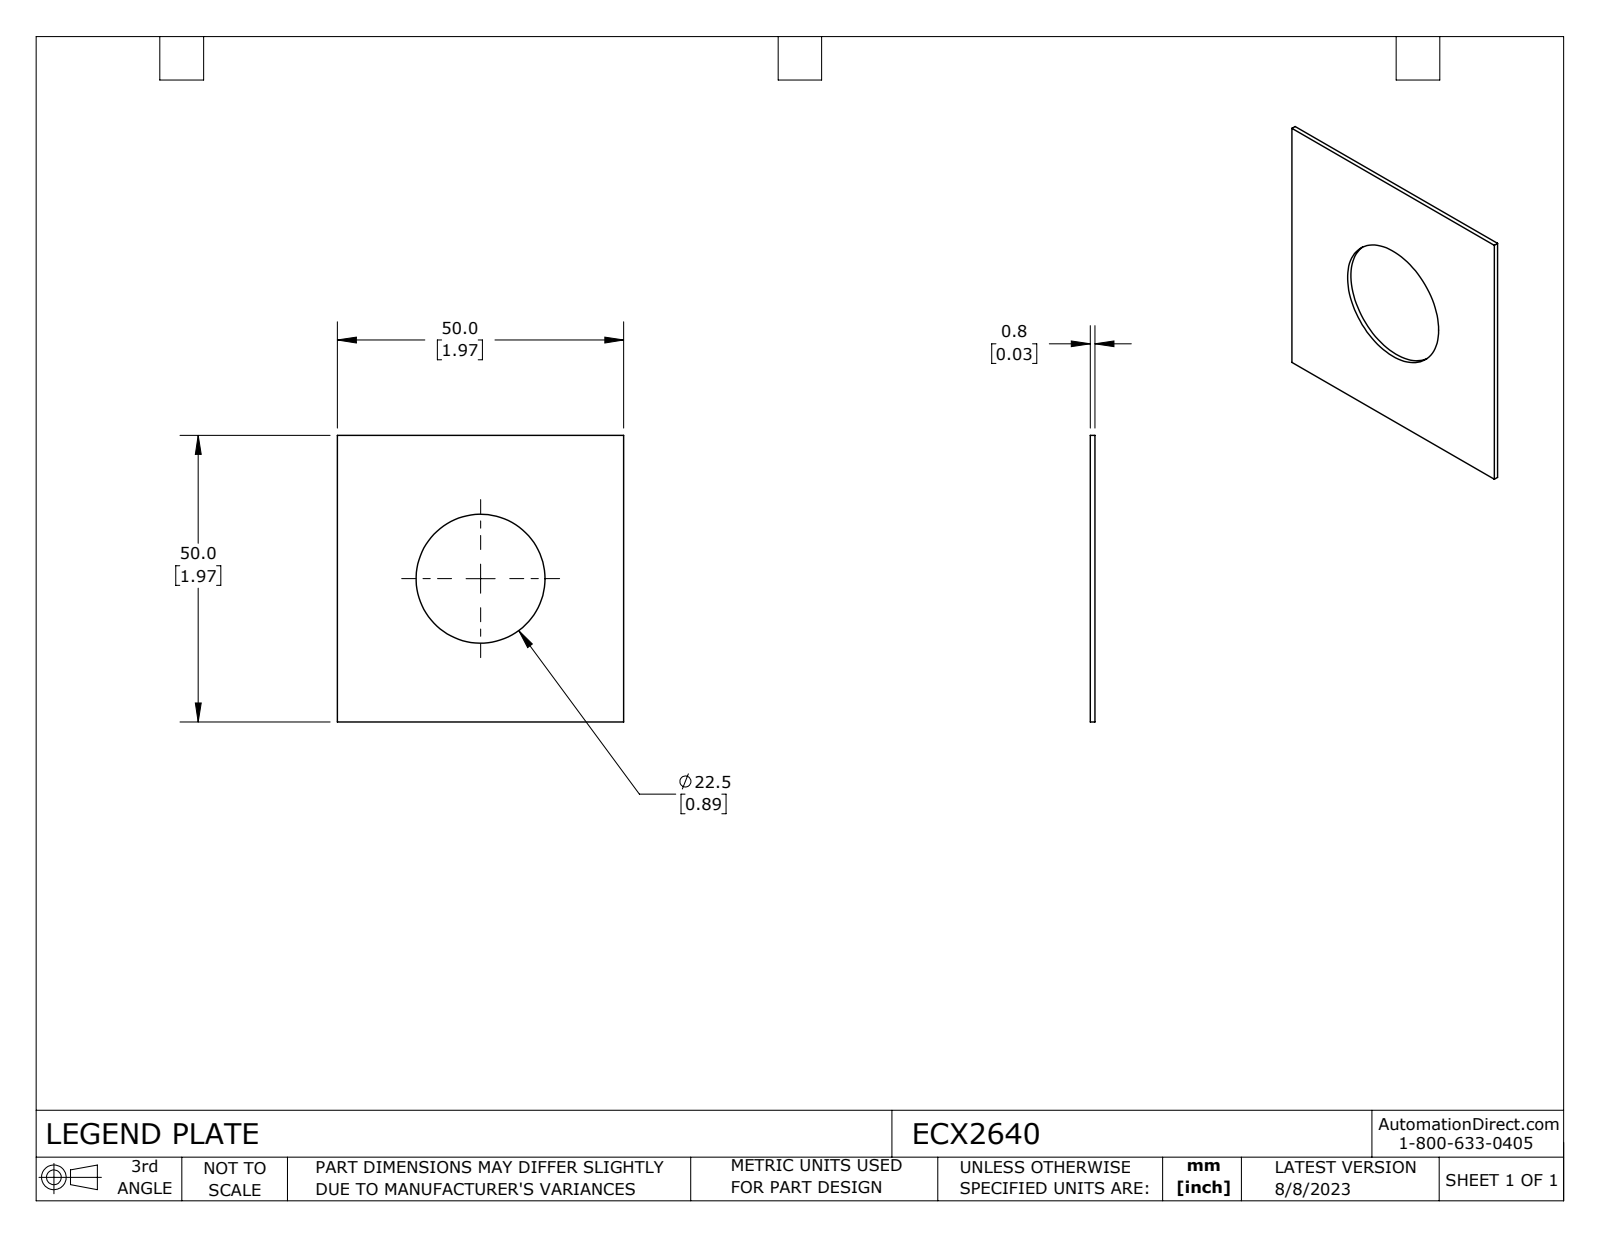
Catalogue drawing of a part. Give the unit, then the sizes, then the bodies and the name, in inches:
Units: inches
Overall size (bounding box): 1.969 × 1.969 × 0.032
Round holes (diameter × count): ⌀0.886 ×1
Main face-to-face distances: 0.032, 1.969
Volume: 0.105 in³ · Surface area: 6.861 in²
Bodies: 1 solid, 8 faces (6 planar, 2 cylindrical, 0 other)
Part name (STEP PRODUCT): ECX2640
STEP written by: SolidWorks 2021 (CONFIG_CONTROL_DESIGN)
